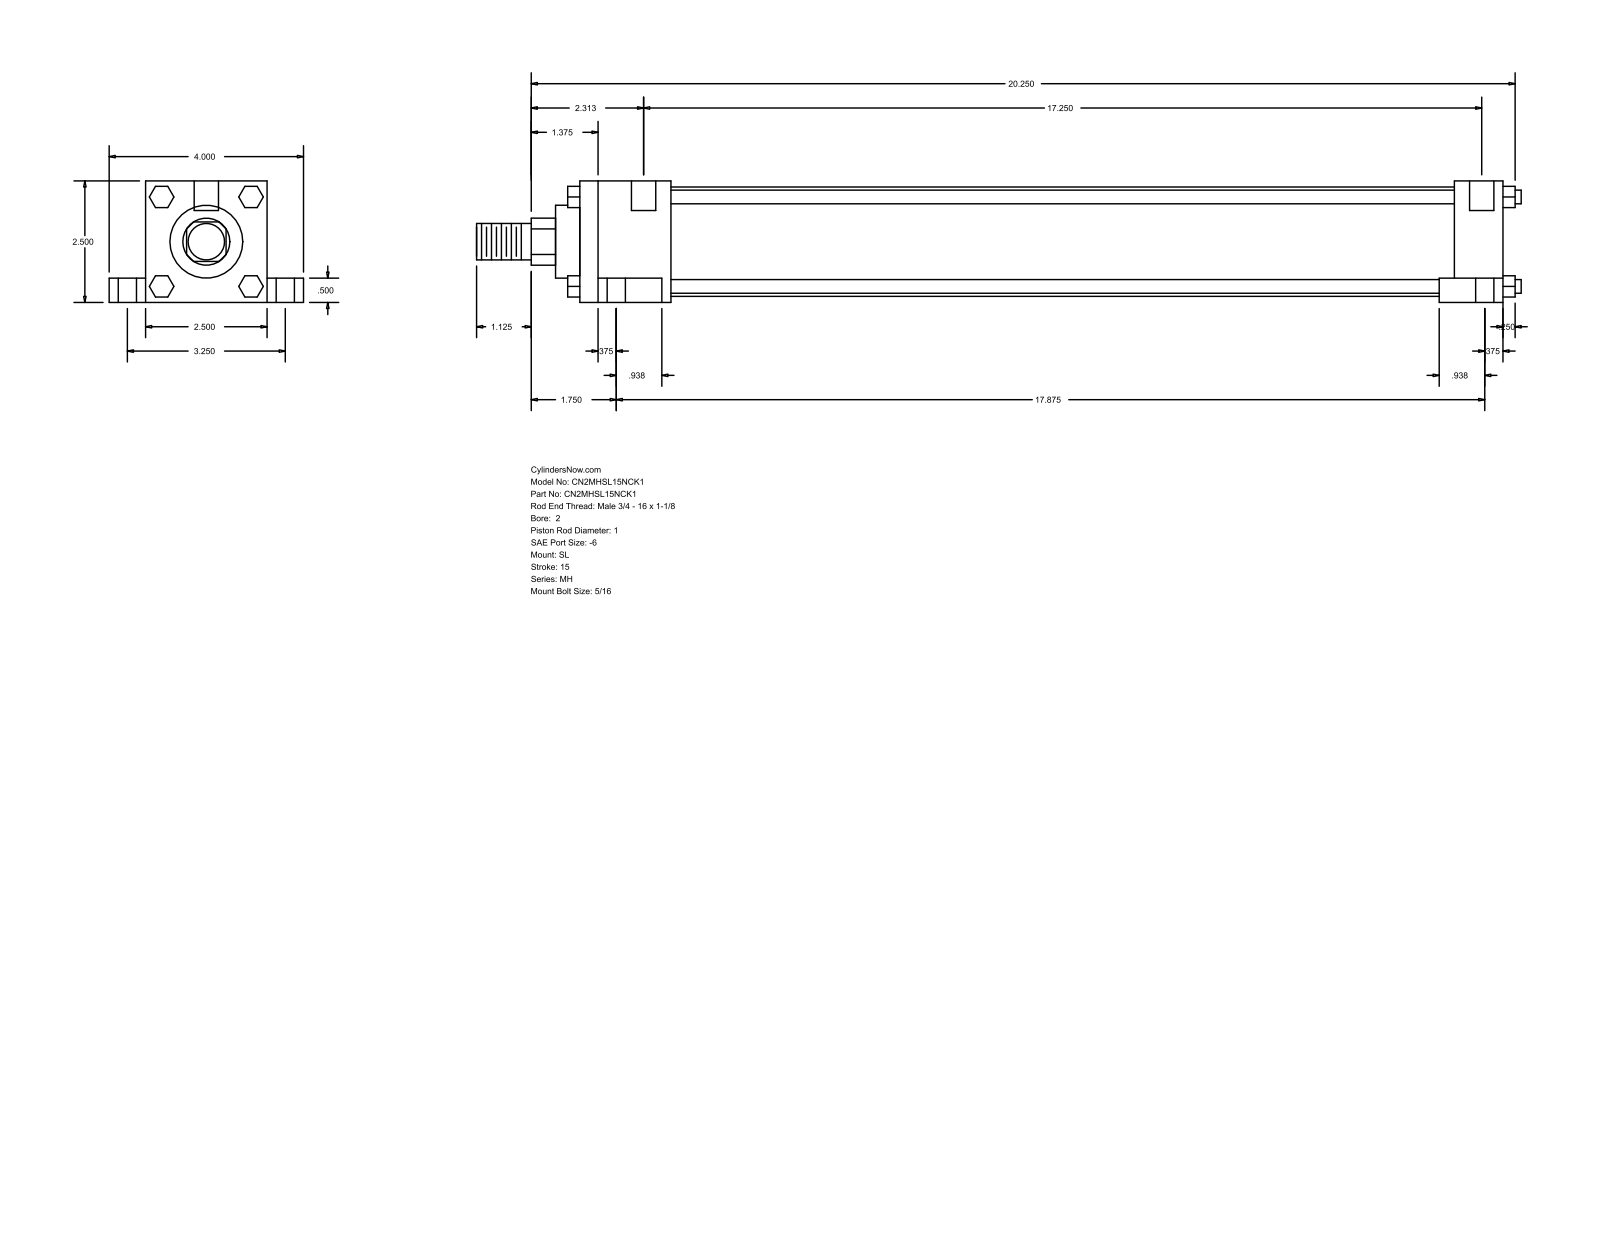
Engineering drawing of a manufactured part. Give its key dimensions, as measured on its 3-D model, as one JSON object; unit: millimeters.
{"part_name": "MH_SL__0200_1", "step_written_by": "GSSL Pune (CONFIG_CONTROL_DESIGN)", "units": "millimeters", "bodies": {"solids": 0, "faces": 148, "planar": 112, "cylindrical": 36, "other": 0}, "overall_size": [546.1, 101.6, 63.5], "round_holes": [[5.56, 4], [9.53, 4], [15.88, 4], [12.7, 2]], "round_bosses_or_shafts": [[7.14, 4], [57.15, 1], [38.1, 1], [25.4, 1], [19.05, 1]], "partial_cylinders_radius": [[12.29, 1]], "face_to_face_distances": [63.5, 482.6, 12.7, 19.05, 50.8, 82.55, 25.4, 457.2, 47.63, 409.57], "hole_center_spacings": [41.3, 42.36, 43.67, 82.54, 441.67, 446.08, 446.41, 454.03]}
